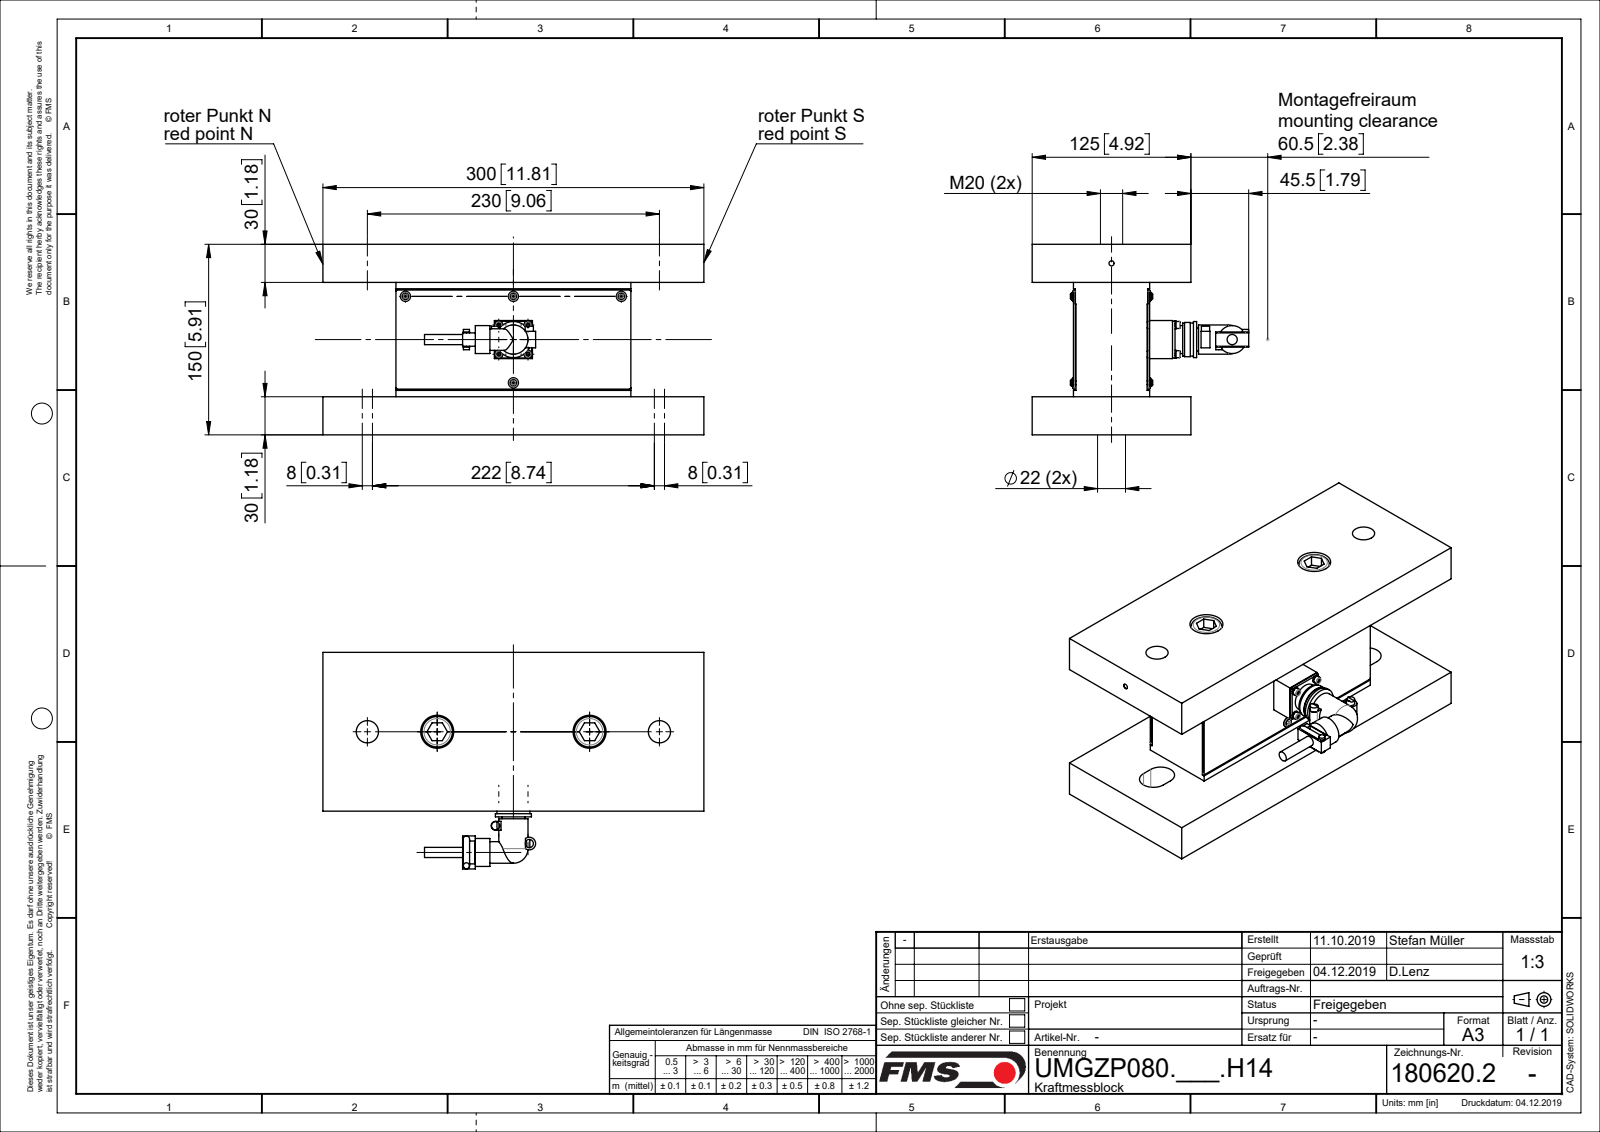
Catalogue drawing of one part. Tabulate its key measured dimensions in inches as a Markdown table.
| quantity | value |
| --- | --- |
| part name | U1806202_STP; U5142704; U51438; U51431 (+8 more) |
| STEP written by | Mechanical Desktop 2009 (CONFIG_CONTROL_DESIGN) |
| units | inches |
| bodies | 36 solids, 685 faces (296 planar, 266 cylindrical, 123 other) |
| overall size | 11.811 × 6.969 × 6.713 |
| volume | 189 in³ |
| surface area | 634.5 in² |
| round holes (diameter × count) | 0.098 × 4, 0.102 × 4, 0.126 × 4, 0.134 × 4, 0.138 × 4, 0.167 × 4, 0.236 × 3, 0.906 × 3, 0.559 × 2, 0.709 × 2, 0.827 × 2, 1.024 × 2 |
| round bosses / shafts (diameter × count) | 0.118 × 8, 0.248 × 4, 0.244 × 4, 0.217 × 4, 1.457 × 2, 0.945 × 2, 0.866 × 2, 0.787 × 2 |
| partial cylindrical surfaces (radius × count) | 0.039 × 4, 0.315 × 4, 0.433 × 4, 0.067 × 2, 0.098 × 2, 0.236 × 2, 0.138 × 1, 0.197 × 1 |
| main face-to-face distances | 1.181, 4.724, 3.543, 5.906, 3.583, 1.339, 1.28, 3.642, 0.059, 2.303 |
| hole center spacings | 0.64, 0.906, 0.995, 1.848, 1.281, 1.339, 2.165, 3.026 |
